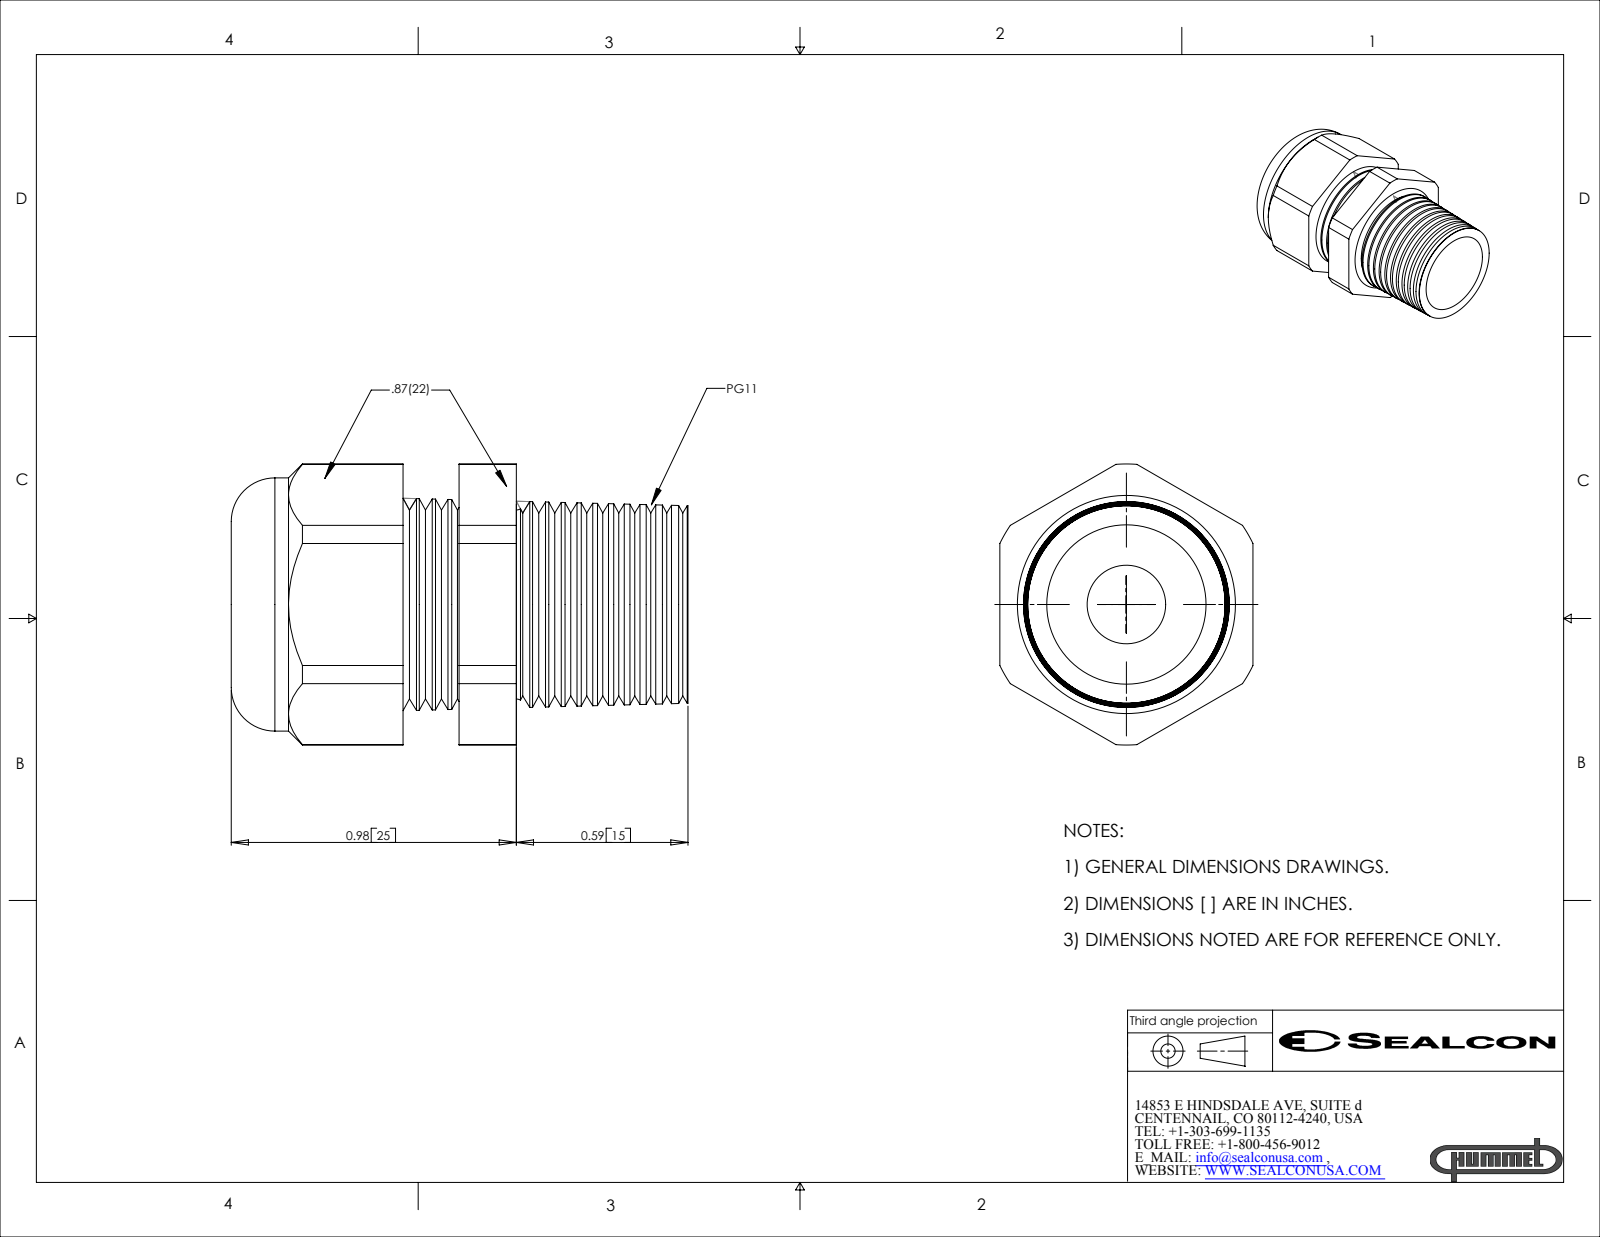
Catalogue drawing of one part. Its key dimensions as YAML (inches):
part_name: "CD11CR-BK"
step_written_by: "SolidWorks 2007 (CONFIG_CONTROL_DESIGN)"
units: inches
bodies: {solids: 2, faces: 148, planar: 20, cylindrical: 22, other: 106}
overall_size: [1.57, 0.966, 0.87]
volume: 0.594
surface_area: 9.303
round_holes:
  - {diameter: 0.27, count: 1}
  - {diameter: 0.547, count: 1}
round_bosses_or_shafts:
  - {diameter: 0.87, count: 1}
partial_cylinders:
  - {radius: 0.483, count: 1}
face_to_face_distances: [0.87, 0.587, 0.394, 0.193, 0.197, 0.783, 0.39, 0.167, 0.56, 0.753]
